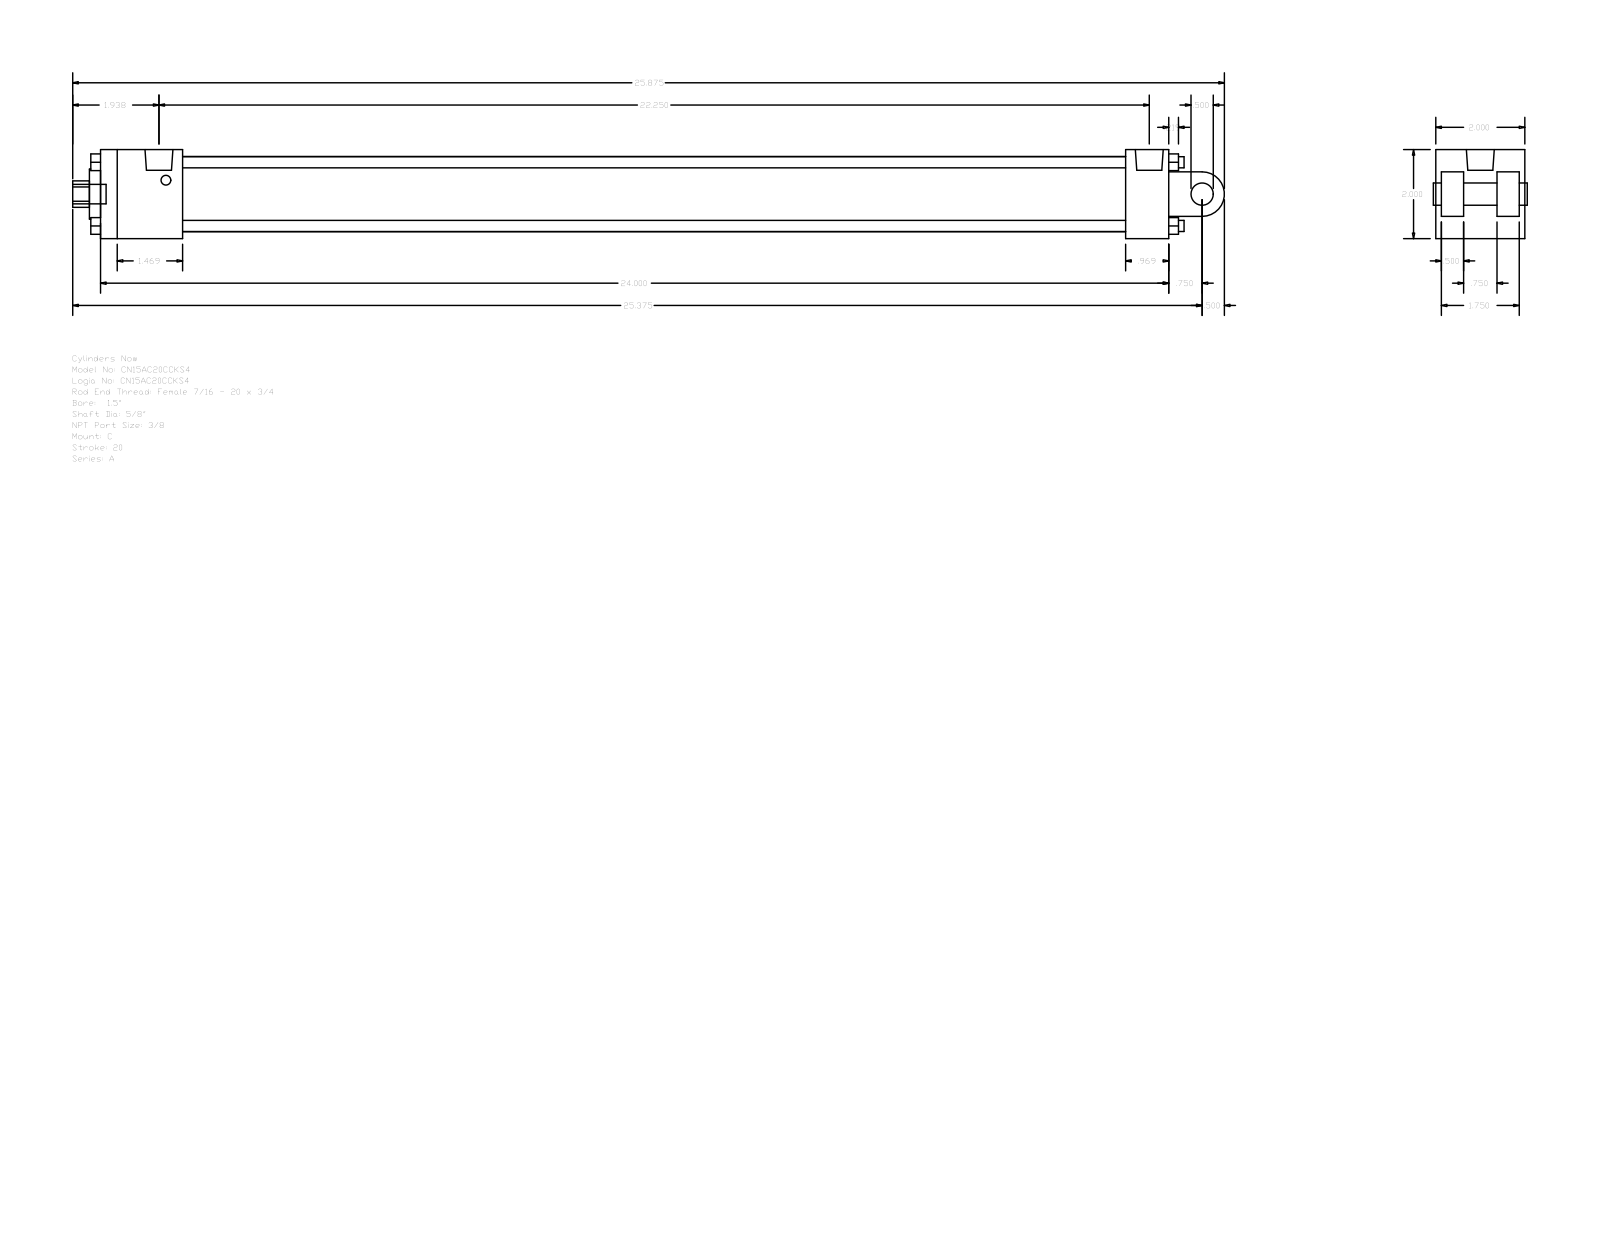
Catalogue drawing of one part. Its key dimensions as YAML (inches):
part_name: "A_C__0150_0.625"
step_written_by: "GSSL Pune (CONFIG_CONTROL_DESIGN)"
units: inches
bodies: {solids: 0, faces: 135, planar: 102, cylindrical: 33, other: 0}
overall_size: [25.875, 2, 2]
round_holes:
  - {diameter: 0.219, count: 2}
  - {diameter: 0.625, count: 1}
  - {diameter: 0.627, count: 1}
  - {diameter: 1.125, count: 1}
  - {diameter: 1.69, count: 1}
round_bosses_or_shafts:
  - {diameter: 0.25, count: 4}
  - {diameter: 0.219, count: 2}
  - {diameter: 0.627, count: 1}
  - {diameter: 0.5, count: 1}
  - {diameter: 0.437, count: 1}
partial_cylinders:
  - {radius: 0.297, count: 1}
  - {radius: 0.5, count: 1}
face_to_face_distances: [2, 0.5, 24, 0.125, 1.875, 0.625, 1.375, 1.25, 23.031, 0.969]
hole_center_spacings: [0.156]
